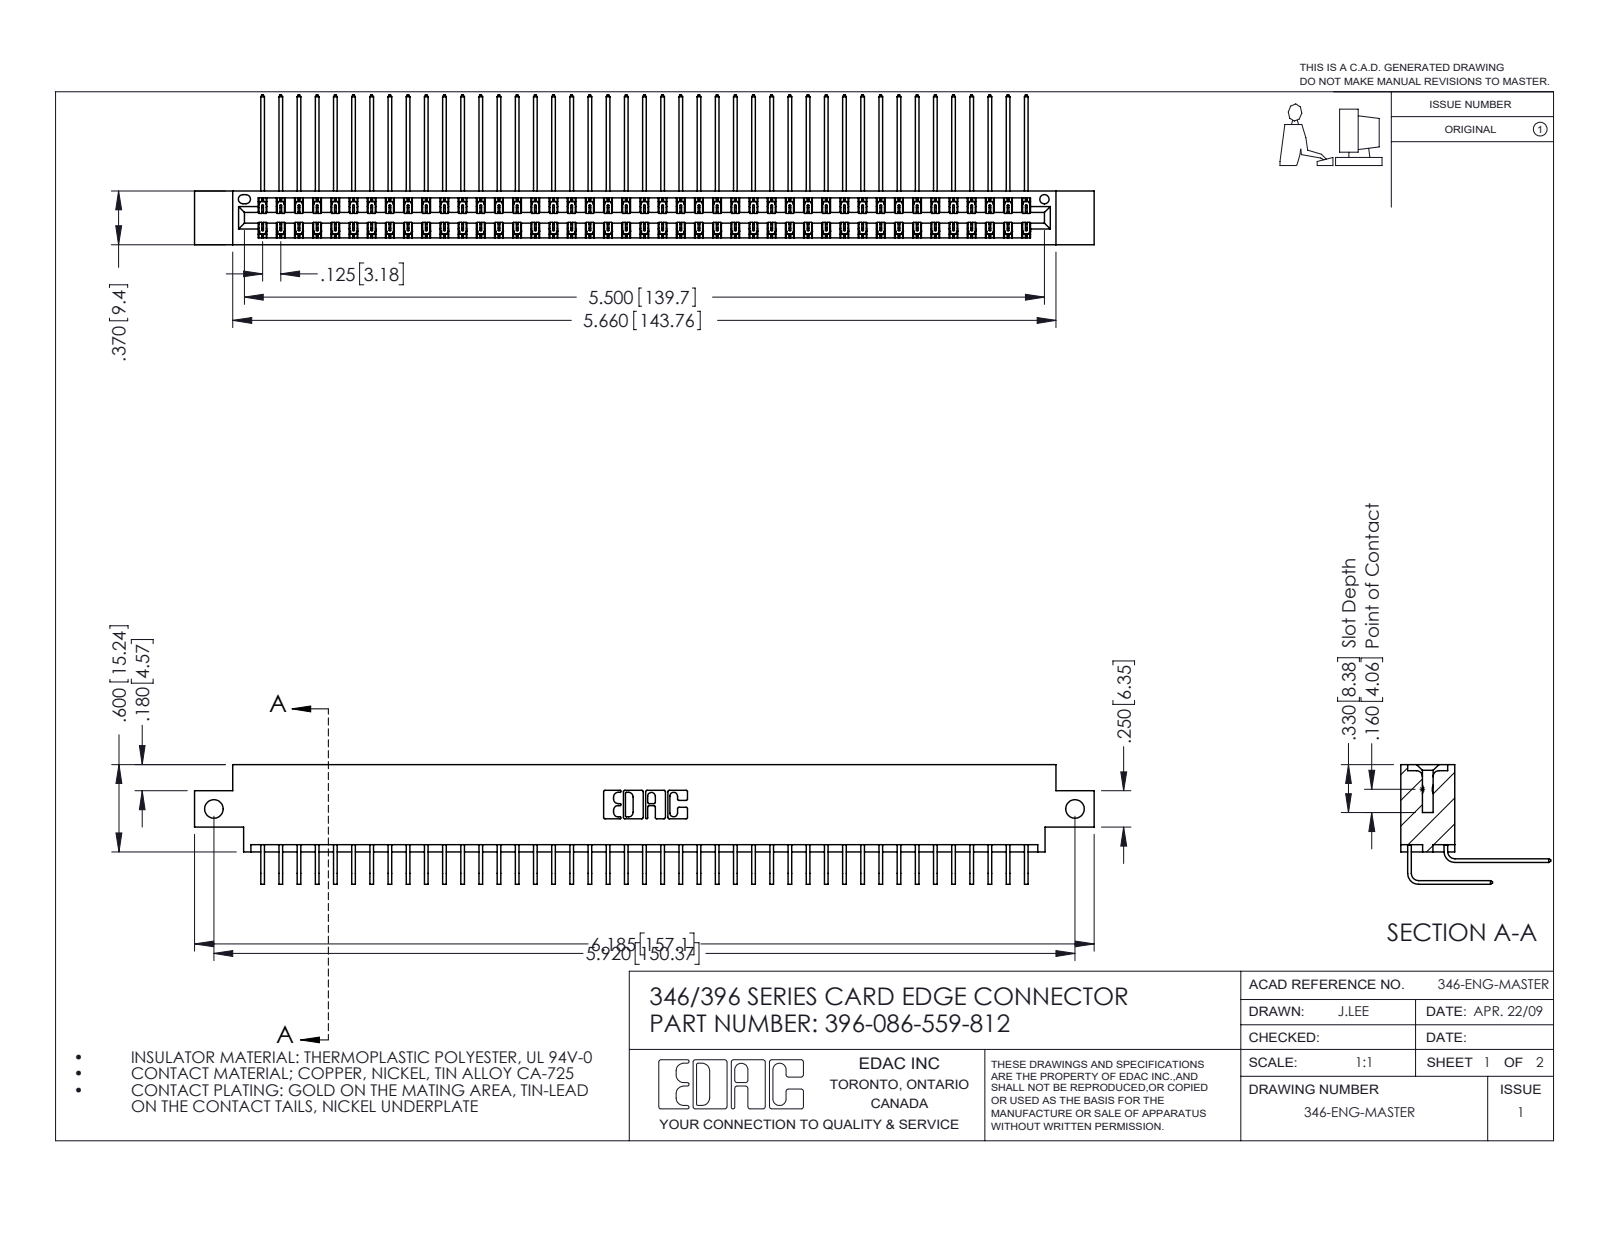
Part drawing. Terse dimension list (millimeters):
name: 396-086-559-812; 345-292-001_558 559 Tail - 1; 346 Part_0.170 Offset - Side Mount; 345-292-001_559 Tail - 2
written by: SolidWorks 2016 (CONFIG_CONTROL_DESIGN)
unit: mm
bodies: 87 solids, 4770 faces (3262 planar, 1508 cylindrical, 0 other)
size: 157.1 × 26.2 × 20.9
volume: 15 600 mm³; area: 23 860 mm²
holes: 2× ⌀3.3, 1× ⌀1.6
rounds: 129× R0.2, 22× R0.3, 6× R0.2, 6× R0.8, 3× R0.7, 2× R0.4, 2× R0.6, 2× R0.6
face distances: 1.2, 8.2, 0.6, 9.4, 6.4, 1.8, 7.6, 7, 3.8, 5.6
hole spacings: 150.4
